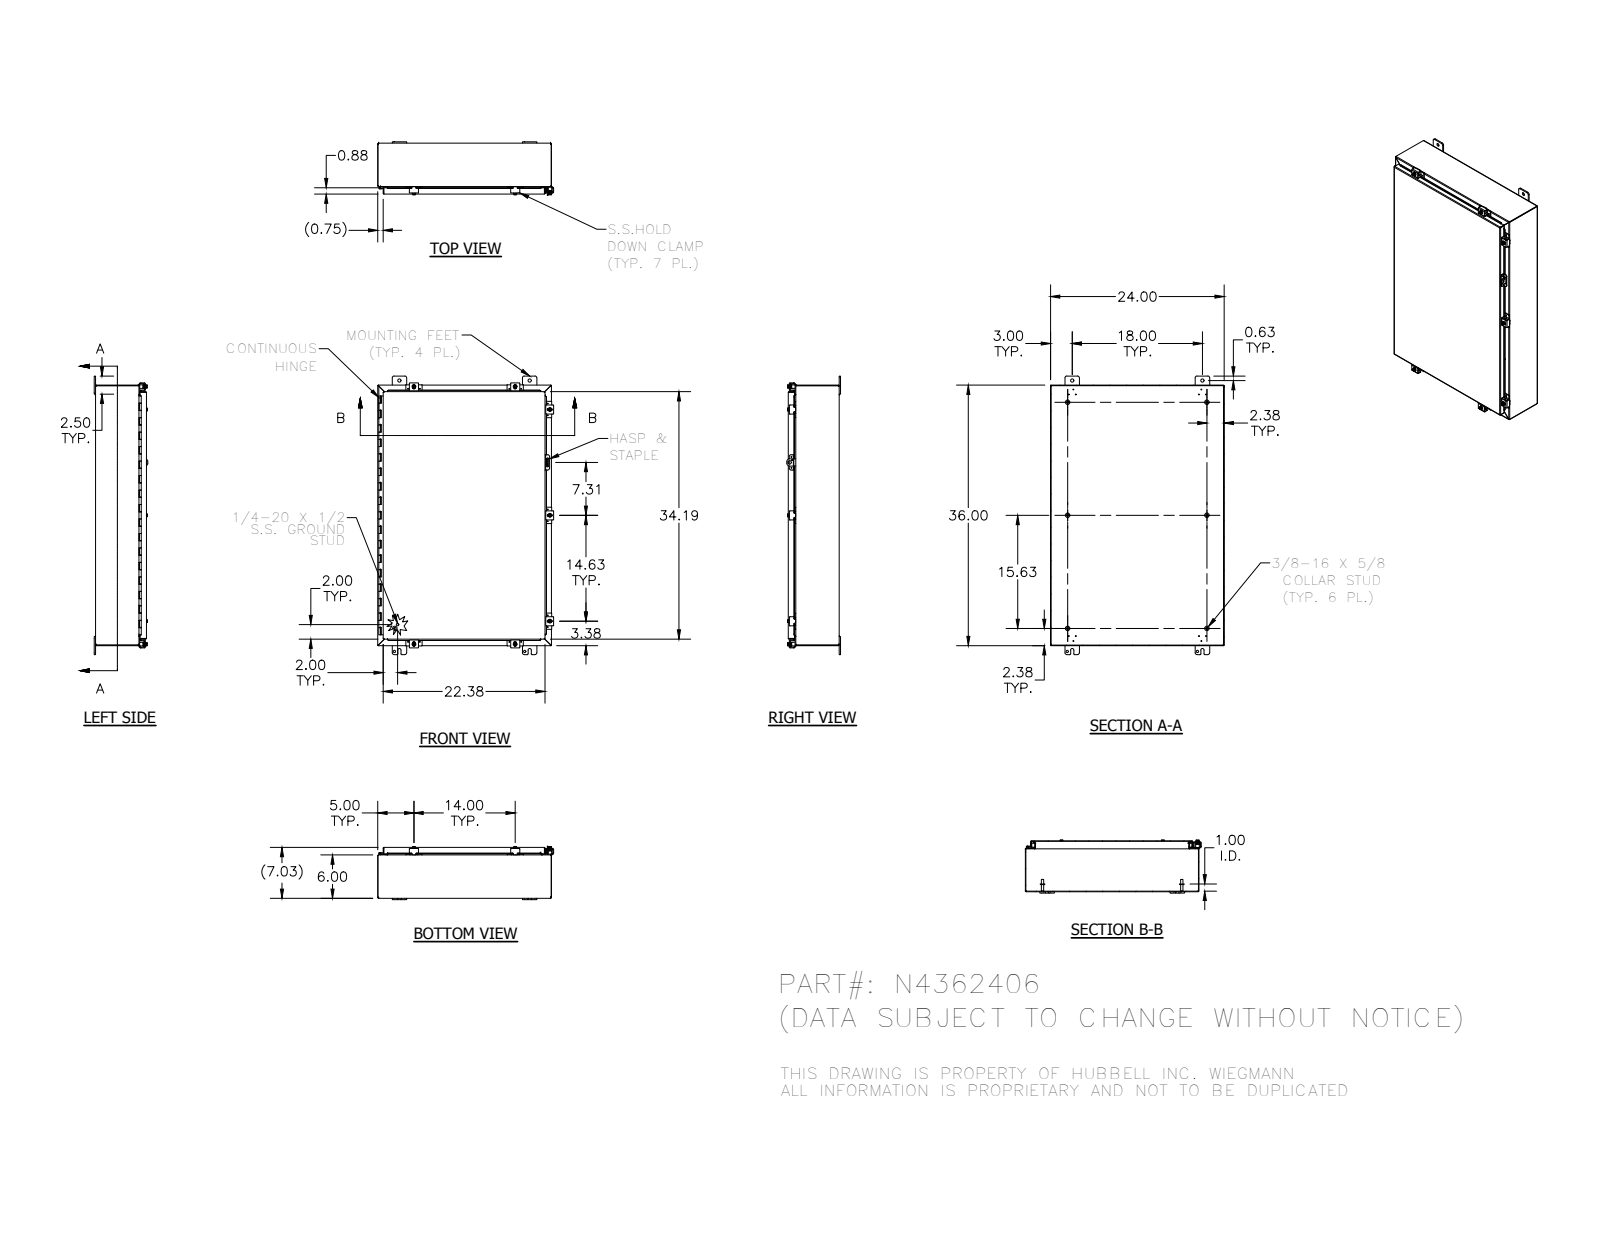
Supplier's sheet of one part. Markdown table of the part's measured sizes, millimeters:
| quantity | value |
| --- | --- |
| part name | 38420_1; N43624LID_1; HFW30825-3_1; 38846_1 (+8 more) |
| STEP written by | SolidWorks 2014 (AUTOMOTIVE_DESIGN) |
| units | millimeters |
| bodies | 54 solids, 2404 faces (930 planar, 1087 cylindrical, 387 other) |
| overall size | 977.9 × 617.5 × 188.2 |
| volume | 3 674 000 mm³ |
| surface area | 3 786 000 mm² |
| round holes (diameter × count) | 2.8 × 17, 3 × 12, 5.4 × 7, 7.1 × 7, 7.6 × 7, 8 × 4, 11.1 × 4, 3.2 × 1, 4 × 1, 12.7 × 1 |
| round bosses / shafts (diameter × count) | 6.4 × 9, 13.2 × 7, 12.7 × 7, 8.9 × 7, 15.9 × 6, 8.4 × 6, 2.9 × 2, 8.6 × 1 |
| partial cylindrical surfaces (radius × count) | 0.8 × 83, 1.6 × 41, 3.2 × 37, 6.4 × 33, 0.8 × 23, 2.7 × 23, 1.6 × 14, 3.6 × 14 |
| main face-to-face distances | 1.9, 176.8, 174.9, 178.6, 607.7, 150.5, 26.2, 912.5, 605.8, 609.6 |
| hole center spacings | 457.2, 22.3, 19.3, 23.9, 24.6, 50.7, 441.2, 465.8 |
